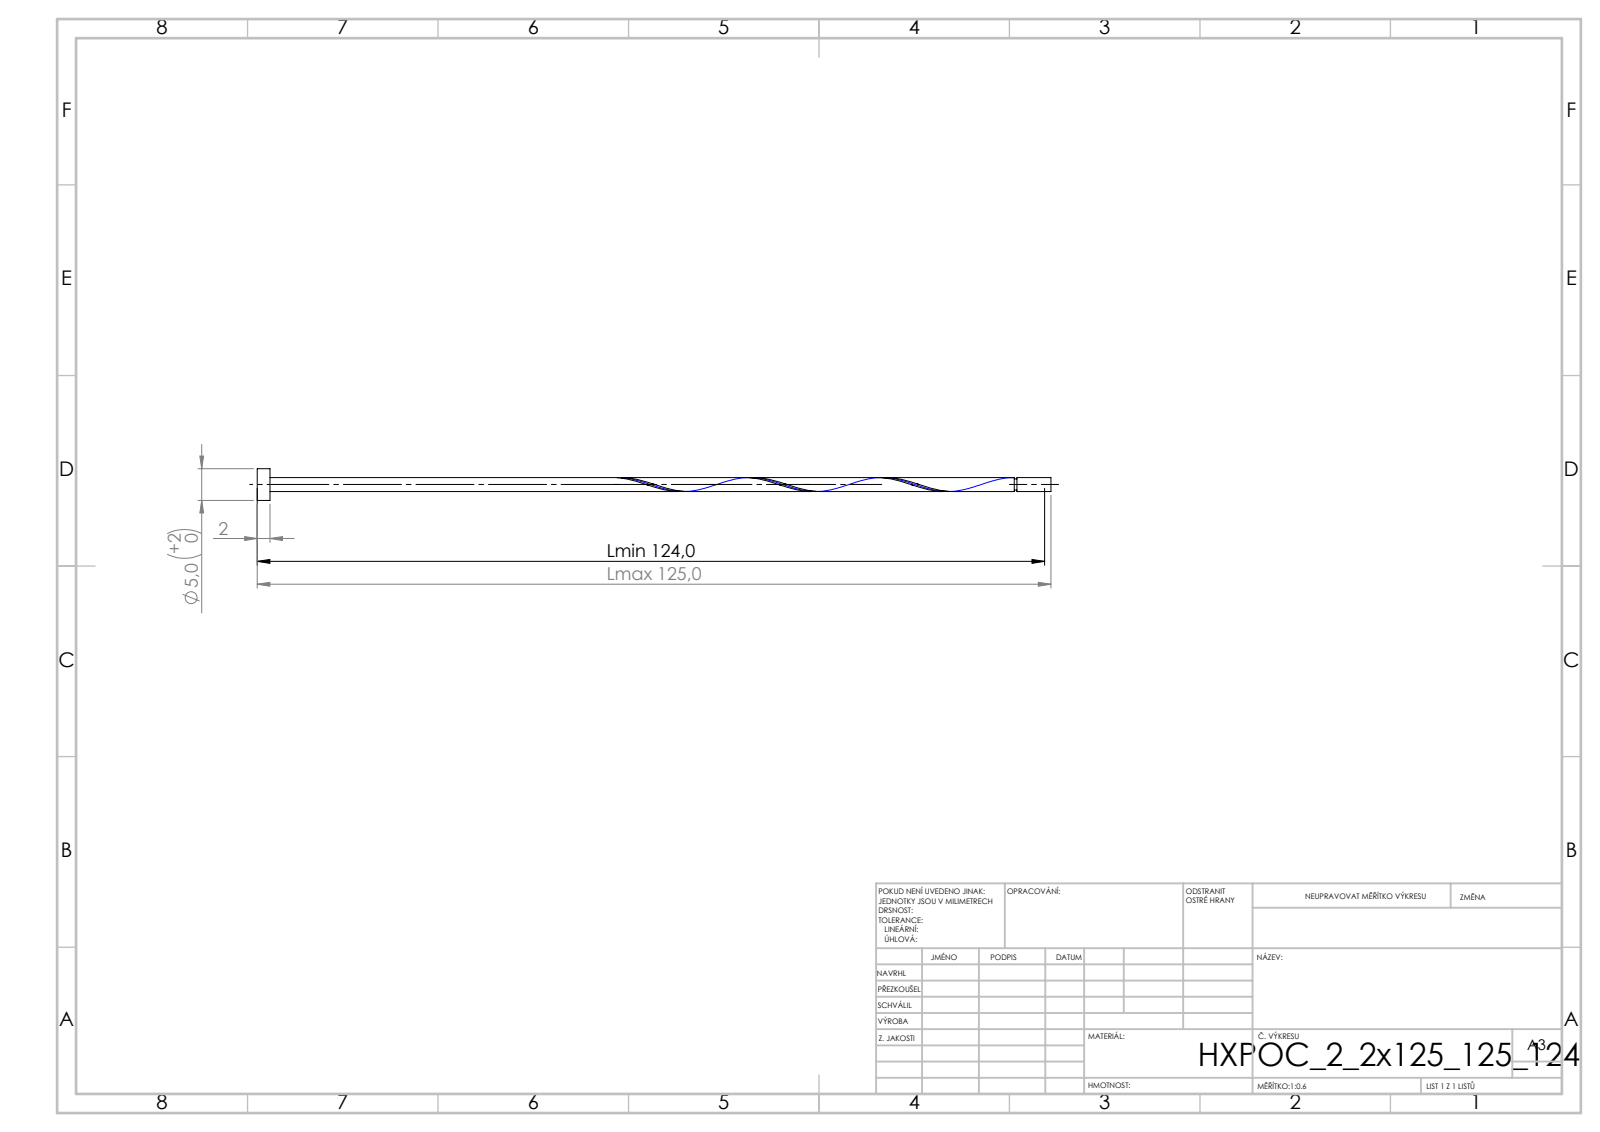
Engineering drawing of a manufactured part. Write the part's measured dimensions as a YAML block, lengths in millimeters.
step_written_by: "SolidWorks 2019 (CONFIG_CONTROL_DESIGN)"
units: millimeters
bodies: {solids: 1, faces: 16, planar: 6, cylindrical: 9, other: 1}
overall_size: [125, 5, 5]
volume: 607
surface_area: 1225
round_bosses_or_shafts:
  - {diameter: 5, count: 1}
  - {diameter: 2.2, count: 1}
  - {diameter: 1.76, count: 1}
face_to_face_distances: [2, 125, 123, 119.65, 117.65, 5.35, 119.21, 117.21, 0.44, 5.79]
